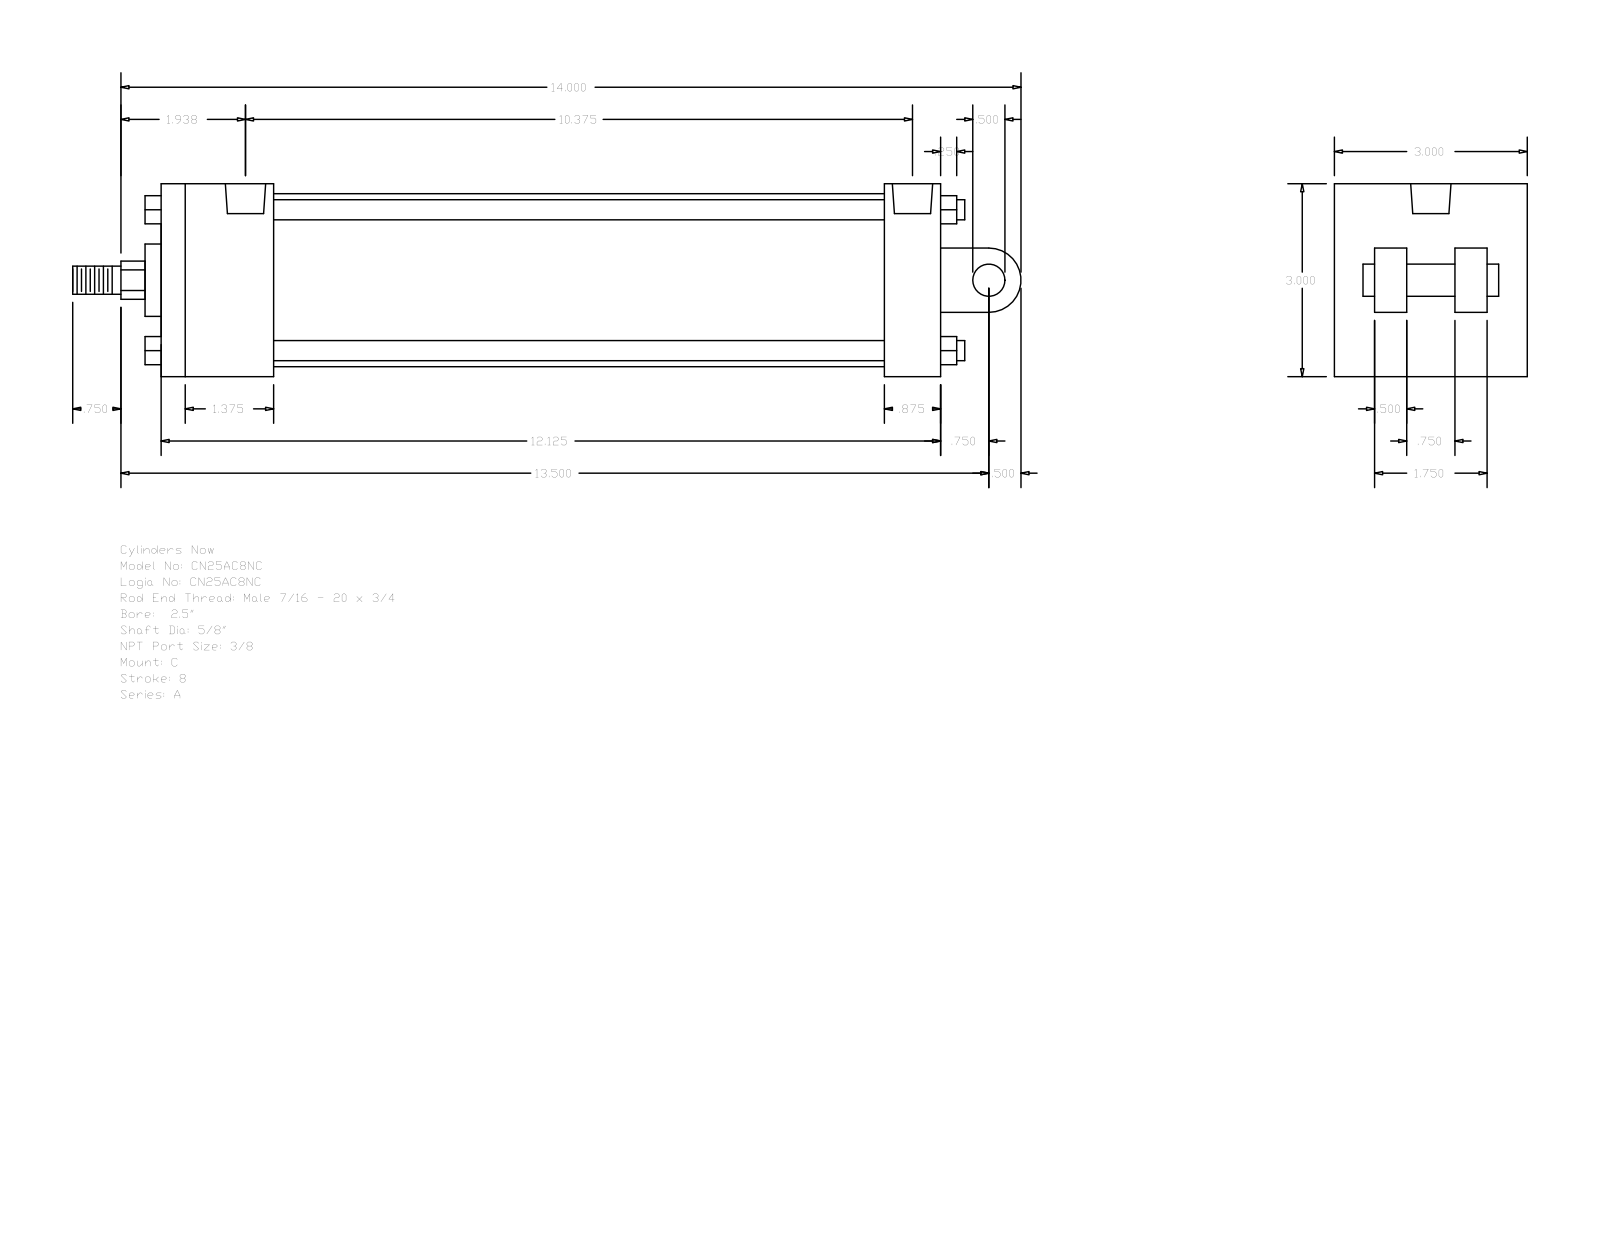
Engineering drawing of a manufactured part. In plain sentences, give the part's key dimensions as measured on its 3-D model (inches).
The part is named "A_C__0250_0.625". Its 3-D file was written by "GSSL Pune (CONFIG_CONTROL_DESIGN)". It is 0 solids with 135 faces: 102 planar, 33 cylindrical and 0 other. Overall it measures 14.75 by 3 by 3 inches. Round holes: 4 of diameter 0.219, 2 of diameter 0.627. Round bosses or shafts: 4 of diameter 0.313, 1 of diameter 2.69, 1 of diameter 1.125, 1 of diameter 0.625, 1 of diameter 0.5, 1 of diameter 0.437. Partial cylindrical surfaces (rounded edges, fillets, slot ends): 1 of radius 0.297, 1 of radius 0.5. The main face-to-face distances are 3, 12.125, 1.75, 11.25, 9.5, 10.375, 0.875, 2, 0.5, 1. The hole center spacings are 0.094, 10.469, 10.563, 10.375.
